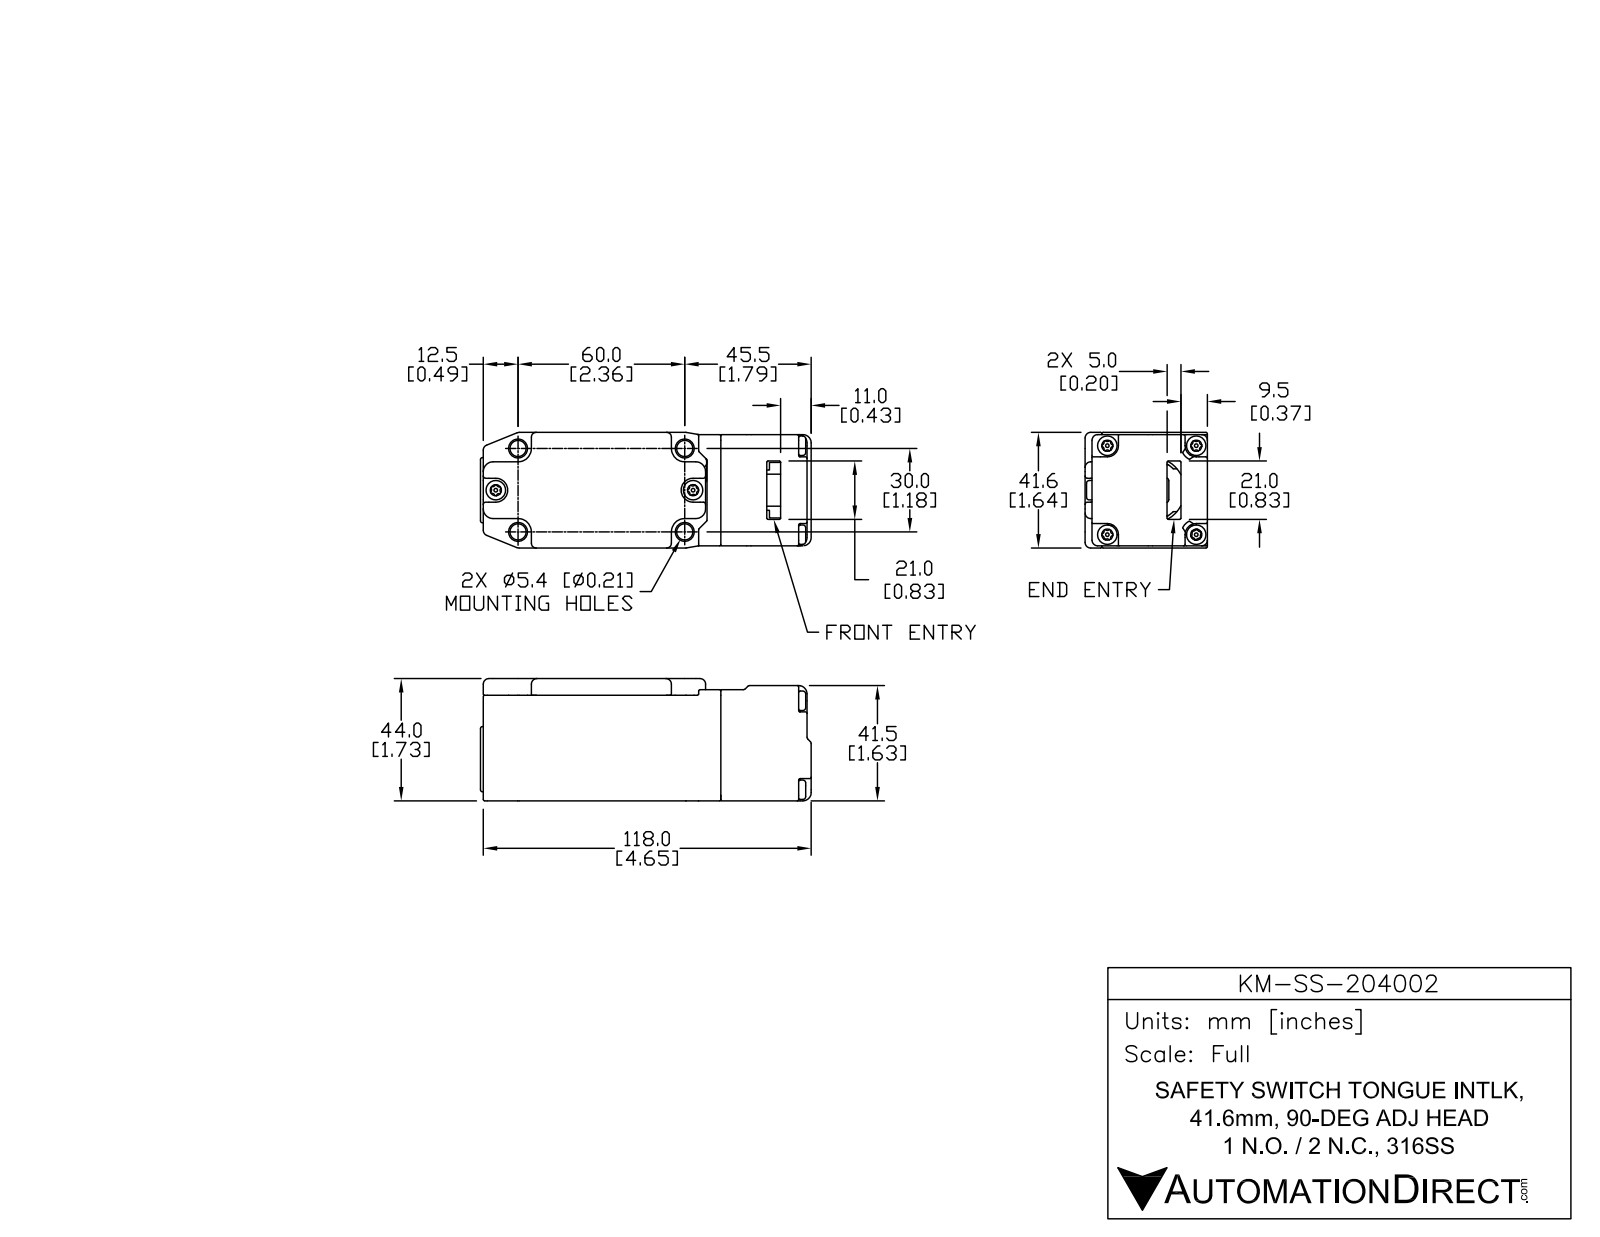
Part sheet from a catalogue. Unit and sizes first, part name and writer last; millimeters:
Units: millimetres
Overall size (bounding box): 119.63 × 44.06 × 41.6
Round holes (diameter × count): ⌀5.4 ×4
Round bosses / shafts (diameter × count): ⌀5.5 ×4, ⌀6.63 ×2, ⌀23 ×1, ⌀5.6 ×1
Partial cylindrical surfaces — rounded edges, fillets, slot ends (radius × count): R0.25 ×134, R0.5 ×43, R5 ×6, R3 ×5, R1 ×4, R1.7 ×4, R2.25 ×2, R2.5 ×2
Main face-to-face distances: 41.6, 0.8, 40.8, 44, 40, 0.5, 43.5, 5, 118, 2.6
Hole centre spacings: 32, 60, 68
Volume: 190 045 mm³ · Surface area: 28 649 mm²
Bodies: 1 solid, 632 faces (120 planar, 278 cylindrical, 234 other)
Part name (STEP PRODUCT): KM-SS-204002
STEP written by: SolidWorks 2013 (AUTOMOTIVE_DESIGN)
